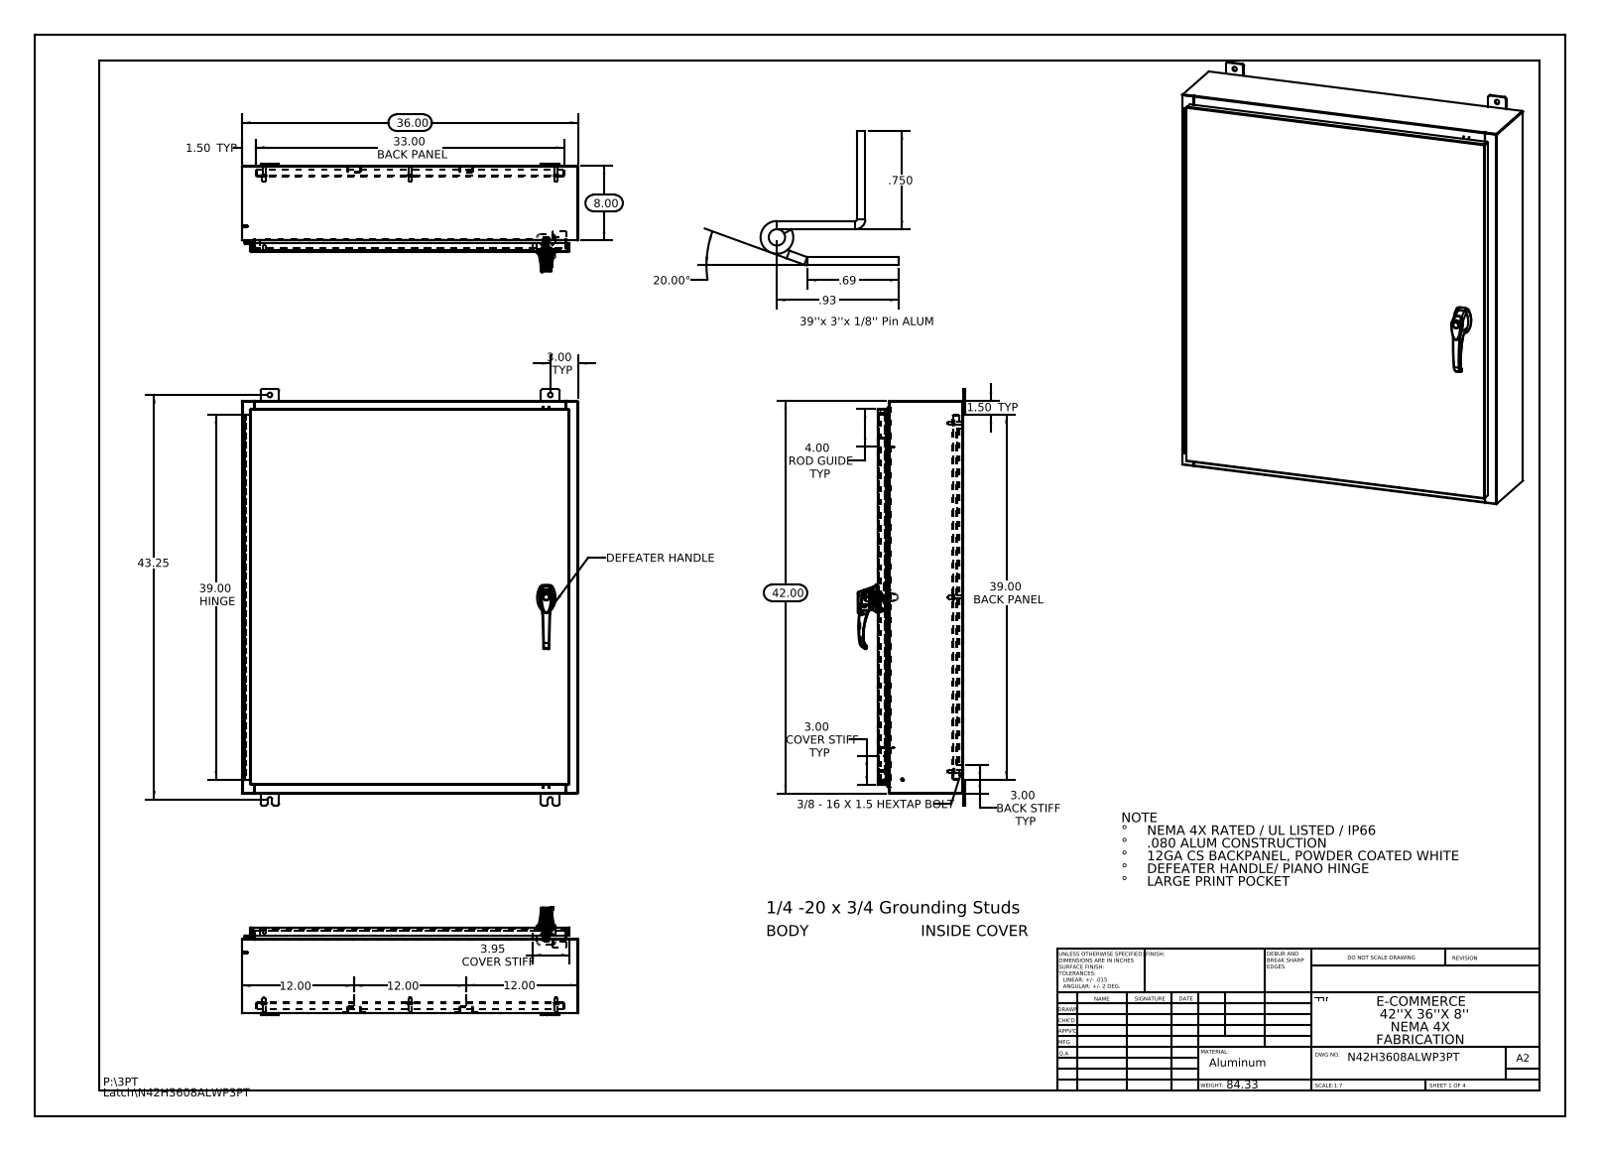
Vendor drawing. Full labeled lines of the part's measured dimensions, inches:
Part name (STEP PRODUCT): 10_30 CD Stud; N42H3608ALWP3PT Bottom; N42H3608ALWP3PT Defeater Handle Stiffener; Quarter-20 CD Stud (+8 more)
STEP written by: SolidWorks 2013 (CONFIG_CONTROL_DESIGN)
Units: inches
Bodies: 51 solids, 3256 faces (1237 planar, 1233 cylindrical, 786 other)
Overall size (bounding box): 44.5 × 36 × 11.495
Volume: 538.6 in³ · Surface area: 13 307 in²
Round holes (diameter × count): ⌀0.5 ×12, ⌀0.25 ×10, ⌀0.138 ×3, ⌀0.161 ×3, ⌀0.079 ×2, ⌀0.203 ×2, ⌀0.313 ×2, ⌀0.437 ×2, ⌀0.125 ×1, ⌀0.125 ×1, ⌀0.197 ×1, ⌀0.276 ×1
Round bosses / shafts (diameter × count): ⌀0.157 ×10, ⌀0.14 ×10, ⌀0.625 ×8, ⌀0.375 ×8, ⌀0.33 ×8, ⌀0.315 ×3, ⌀0.236 ×3, ⌀1.181 ×1
Partial cylindrical surfaces — rounded edges, fillets, slot ends (radius × count): R0.118 ×37, R0.013 ×34, R0.006 ×33, R0.088 ×28, R0.19 ×24, R0.039 ×15, R0.028 ×12, R0.008 ×6
Main face-to-face distances: 0.075, 9.126, 9.051, 9.201, 0.104, 1, 8.126, 1.075, 8.051, 1.179
Hole centre spacings: 14.36, 16.667, 18.625, 24.311, 36.379, 40.394, 31.25, 37.25
